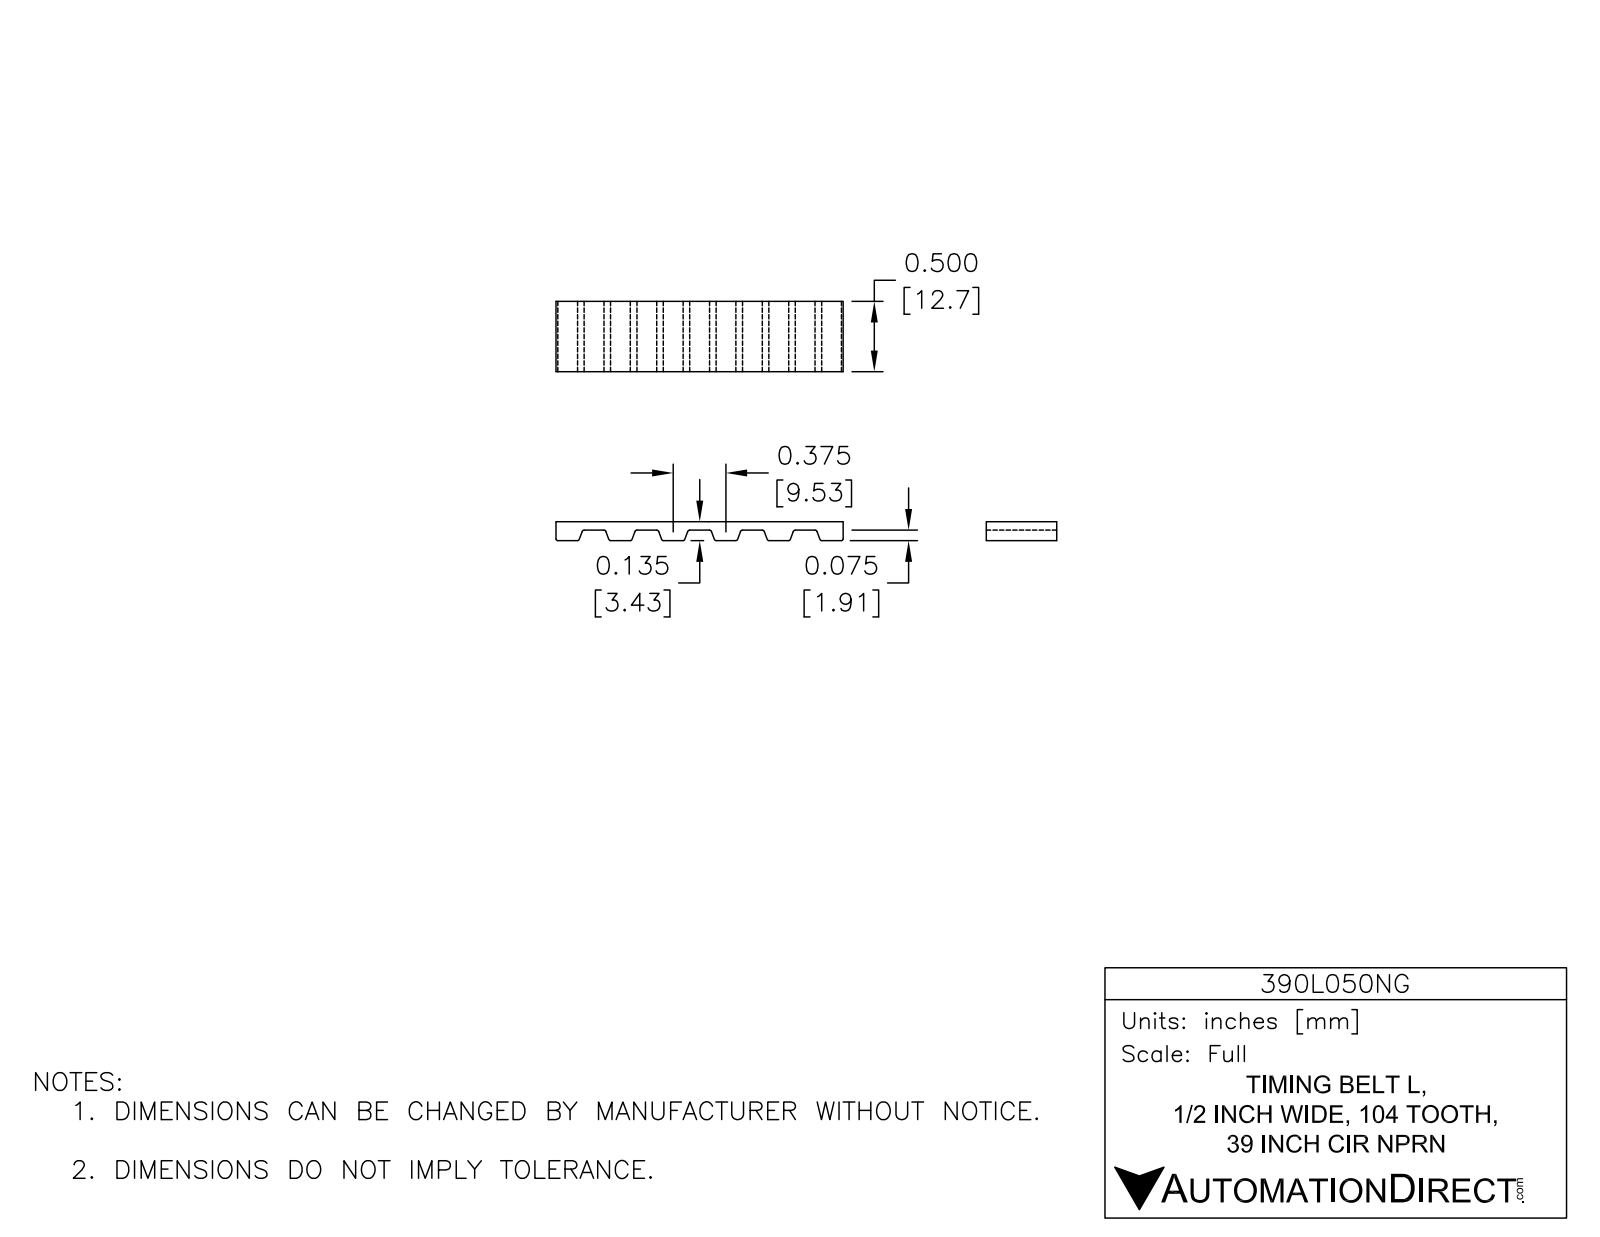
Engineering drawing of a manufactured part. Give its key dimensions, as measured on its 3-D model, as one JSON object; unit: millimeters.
{"part_name": "390L050NG", "step_written_by": "SolidWorks 2014 (AUTOMOTIVE_DESIGN)", "units": "millimeters", "bodies": {"solids": 1, "faces": 847, "planar": 393, "cylindrical": 454, "other": 0}, "overall_size": [451.8, 76.2, 12.7], "volume_mm3": 28960, "surface_area_mm2": 32600, "partial_cylinders_radius": [[0.5, 412], [36.4, 2], [38.1, 2]], "face_to_face_distances": [1.7, 74.5, 76.2, 72.9, 12.7, 3.6, 72.6, 1.9, 71, 69.1]}
